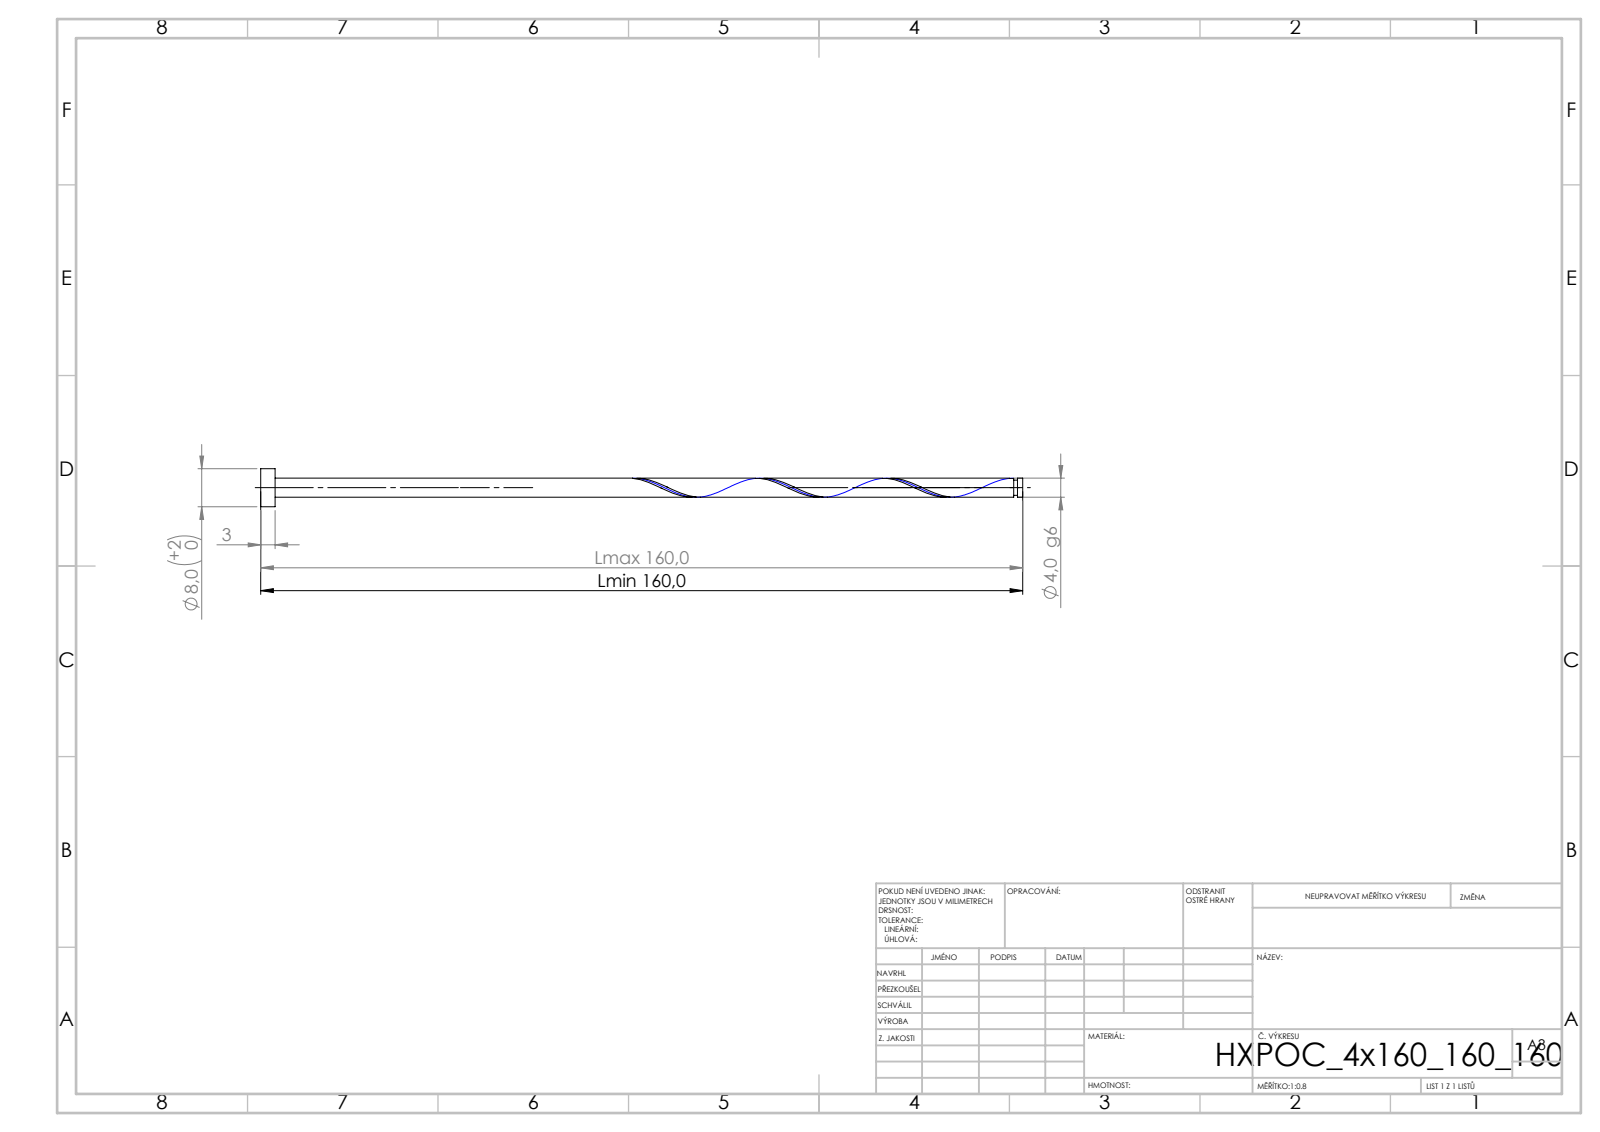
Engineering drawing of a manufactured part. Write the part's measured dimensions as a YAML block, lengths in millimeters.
step_written_by: "SolidWorks 2019 (CONFIG_CONTROL_DESIGN)"
units: millimeters
bodies: {solids: 1, faces: 21, planar: 6, cylindrical: 14, other: 1}
overall_size: [160, 8, 8]
volume: 2101
surface_area: 2191
round_bosses_or_shafts:
  - {diameter: 8, count: 1}
  - {diameter: 4, count: 1}
  - {diameter: 3.2, count: 1}
face_to_face_distances: [3, 160, 157, 158.91, 155.91, 1.09, 158.11, 155.11, 0.8, 1.89]
